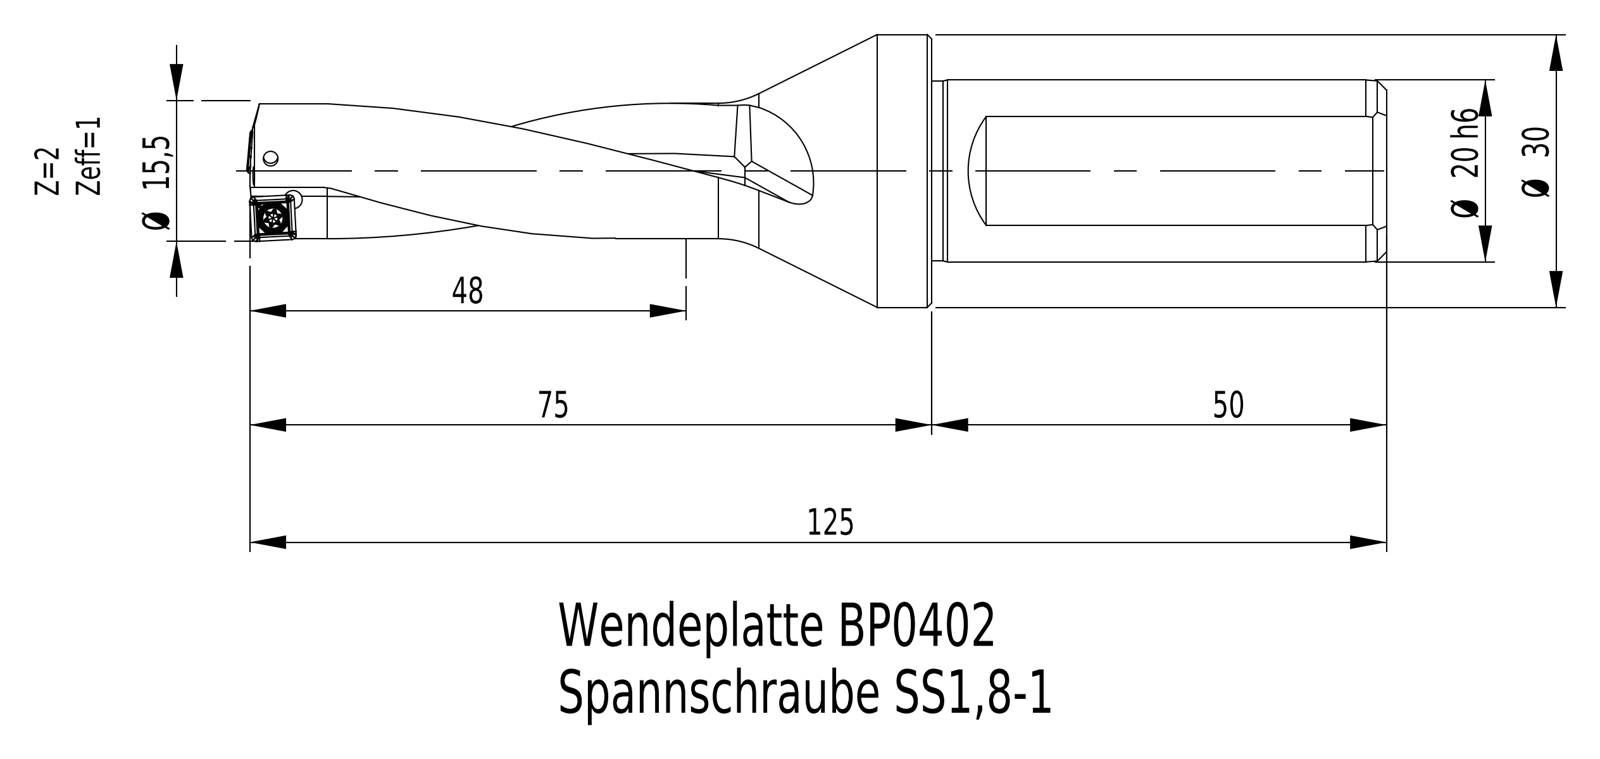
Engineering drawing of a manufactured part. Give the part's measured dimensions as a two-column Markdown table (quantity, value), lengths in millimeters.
| quantity | value |
| --- | --- |
| part name | BW-15,5-48-20-04 |
| STEP written by | SolidWorks 2015 (AUTOMOTIVE_DESIGN) |
| units | millimeters |
| bodies | 1 solid, 45 faces (7 planar, 14 cylindrical, 24 other) |
| overall size | 124.95 × 30 × 30 |
| volume | 34 043 mm³ |
| surface area | 9 070 mm² |
| round holes (diameter × count) | 2.7 × 1, 4 × 1 |
| round bosses / shafts (diameter × count) | 30 × 1, 20 × 1, 19.8 × 1, 15.5 × 1, 14.9 × 1 |
| main face-to-face distances | 50, 74.95, 124.95, 30.05, 5, 69.95, 119.95 |
